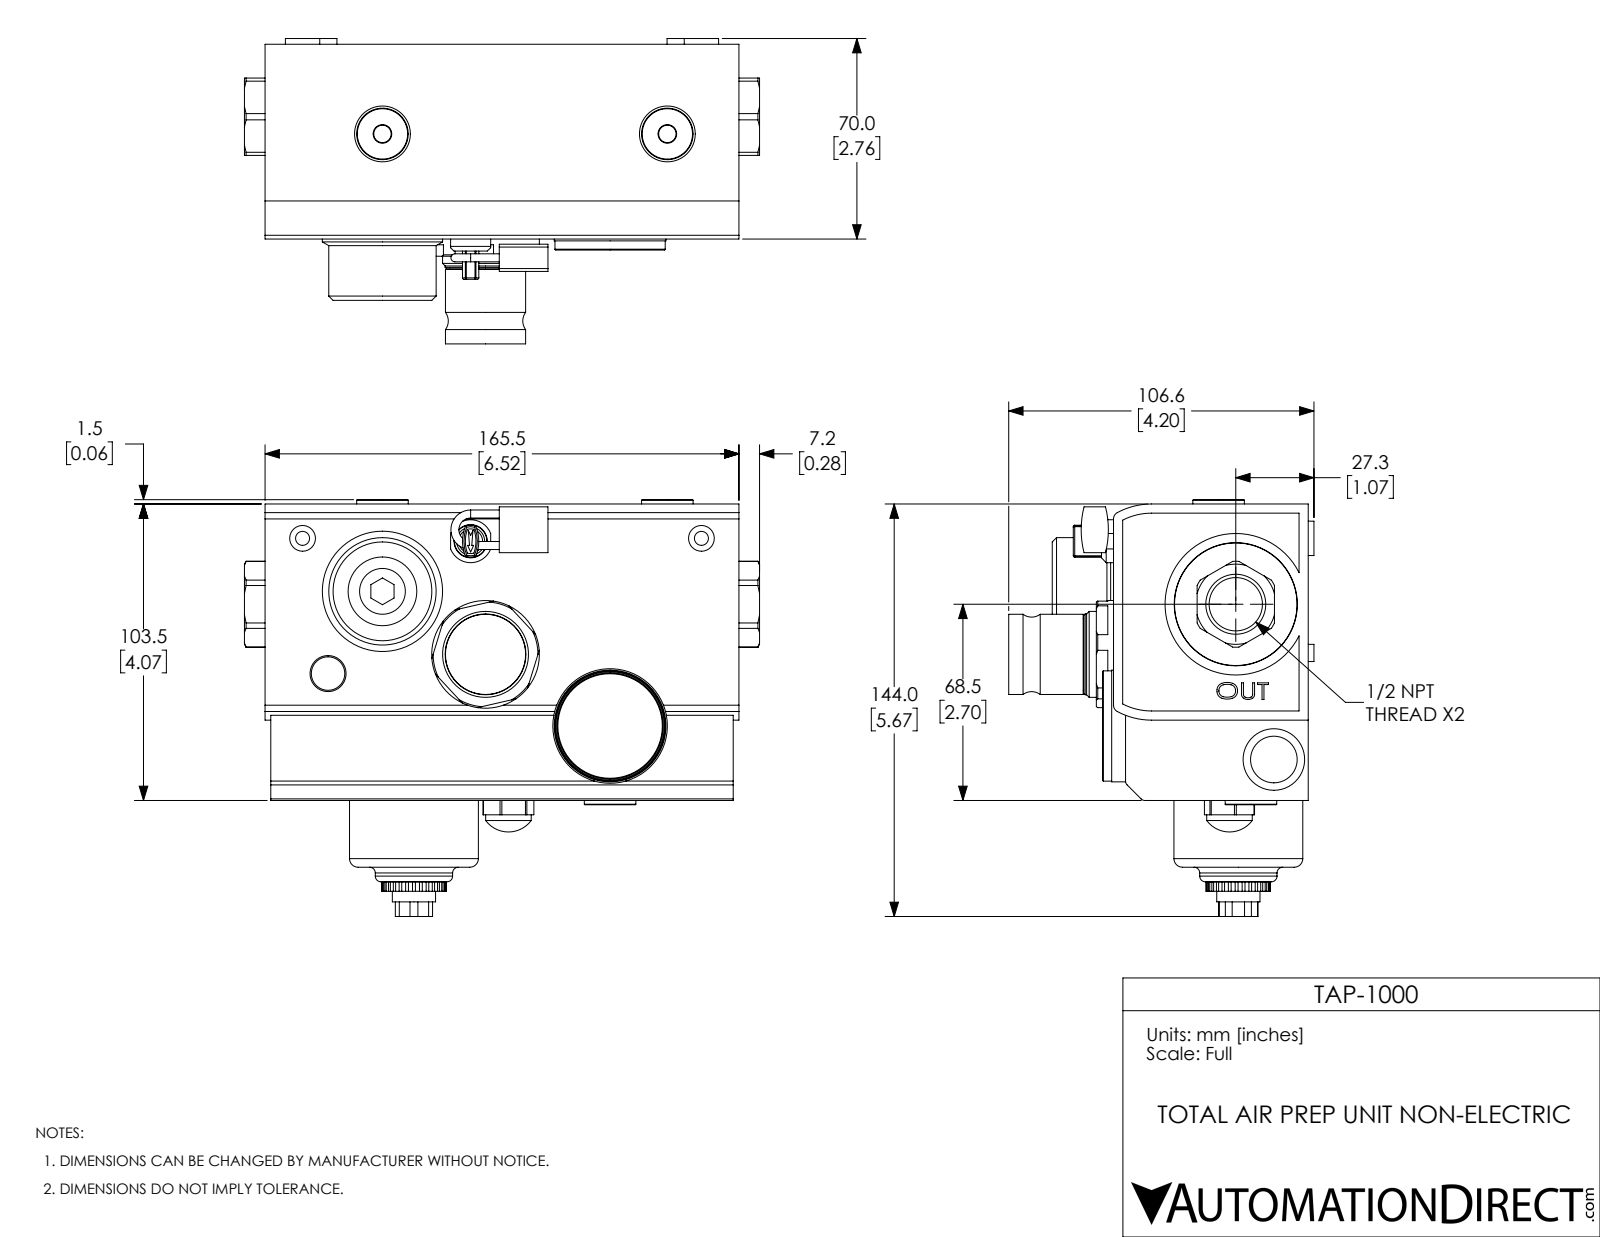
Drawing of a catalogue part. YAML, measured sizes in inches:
part_name: "TAP-1000"
step_written_by: "SolidWorks 2017 (AUTOMOTIVE_DESIGN)"
units: inches
bodies: {solids: 8, faces: 581, planar: 186, cylindrical: 281, other: 114}
overall_size: [7.083, 5.728, 4.197]
volume: 73.93
surface_area: 170.4
round_holes:
  - {diameter: 0.24, count: 3}
  - {diameter: 0.768, count: 3}
  - {diameter: 0.098, count: 2}
  - {diameter: 0.193, count: 2}
  - {diameter: 0.256, count: 2}
  - {diameter: 0.354, count: 2}
  - {diameter: 0.518, count: 2}
  - {diameter: 0.337, count: 1}
  - {diameter: 0.488, count: 1}
  - {diameter: 0.496, count: 1}
  - {diameter: 0.518, count: 1}
  - {diameter: 0.734, count: 1}
round_bosses_or_shafts:
  - {diameter: 0.709, count: 3}
  - {diameter: 0.437, count: 3}
  - {diameter: 0.472, count: 2}
  - {diameter: 0.236, count: 2}
  - {diameter: 0.11, count: 2}
  - {diameter: 1.945, count: 1}
  - {diameter: 1.772, count: 1}
  - {diameter: 1.685, count: 1}
partial_cylinders:
  - {radius: 0.071, count: 29}
  - {radius: 0.098, count: 6}
  - {radius: 0.02, count: 4}
  - {radius: 0.079, count: 4}
  - {radius: 0.229, count: 4}
  - {radius: 0.282, count: 4}
  - {radius: 0.039, count: 2}
  - {radius: 0.059, count: 2}
face_to_face_distances: [2.677, 4.075, 0.039, 0.047, 6.35, 0.087, 6.39, 6.303, 0.126, 6.437]
hole_center_spacings: [1.614, 5.366, 0.283, 0.511, 0.904, 1.127, 1.318, 1.349]
